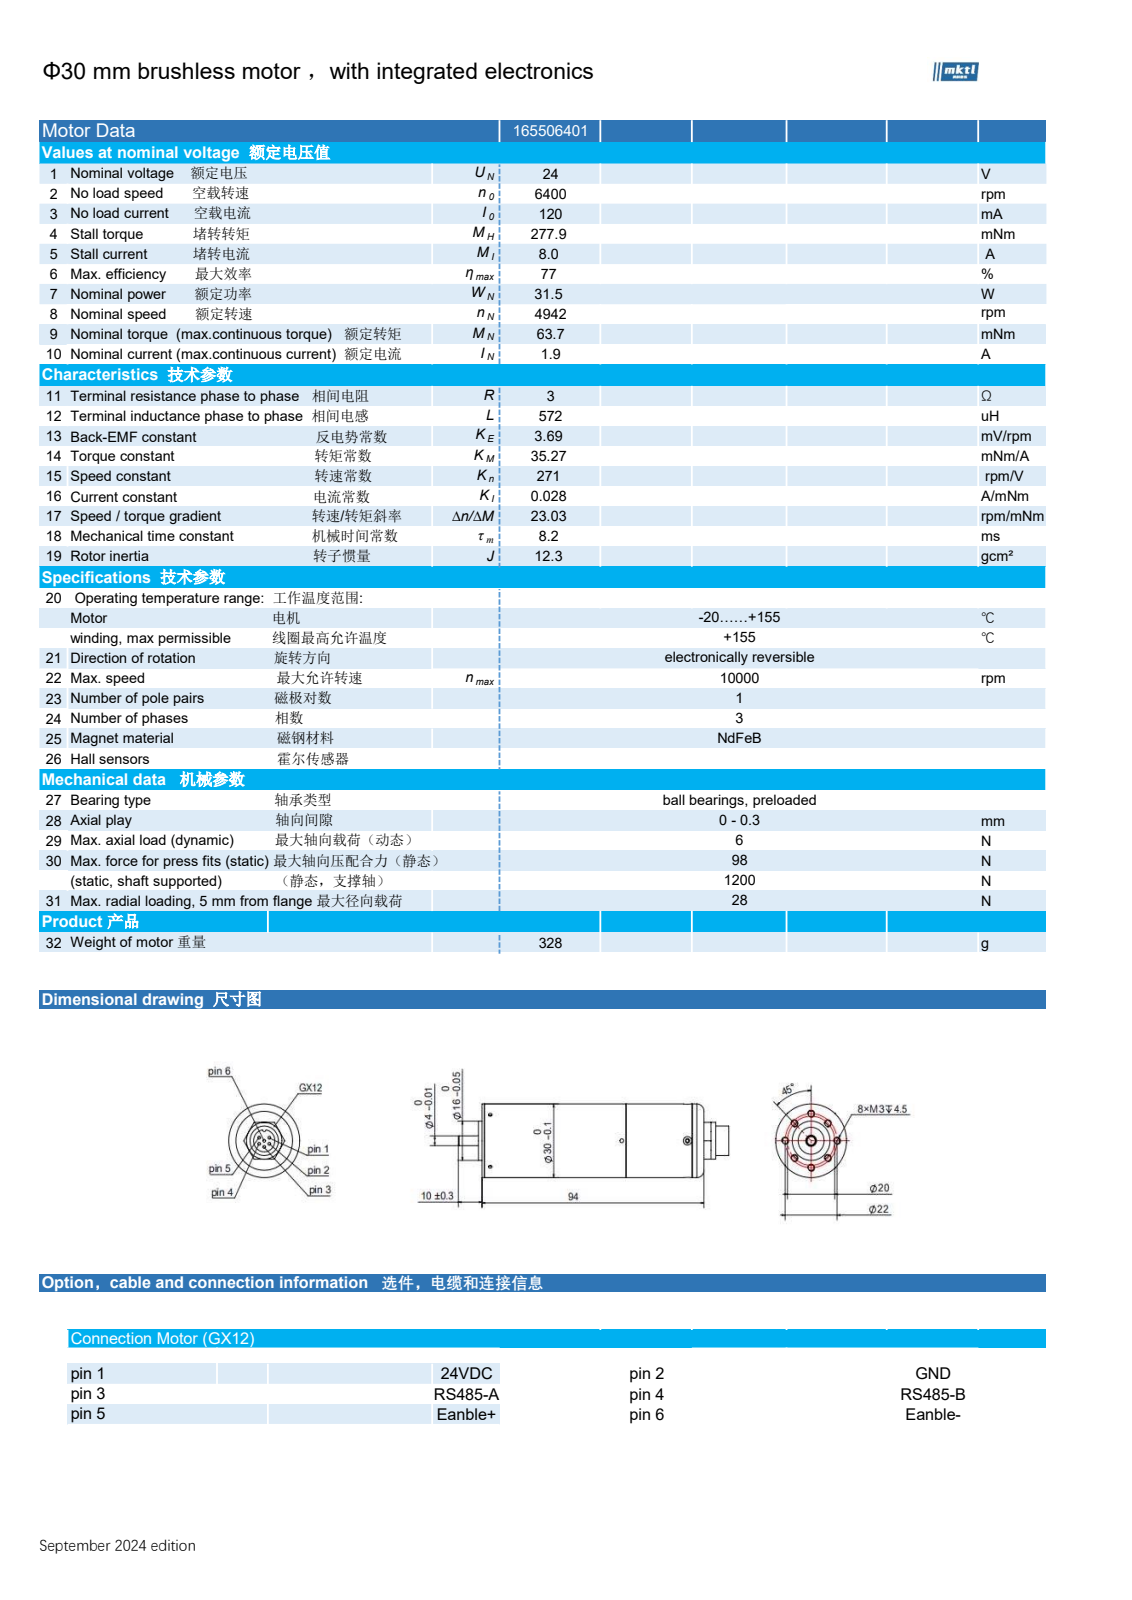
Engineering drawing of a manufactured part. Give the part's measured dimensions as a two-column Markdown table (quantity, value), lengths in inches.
| quantity | value |
| --- | --- |
| part name | approval 165506401 |
| STEP written by | SolidWorks 2018 (CONFIG_CONTROL_DESIGN) |
| units | inches |
| bodies | 240 solids, 1781 faces (558 planar, 1149 cylindrical, 74 other) |
| overall size | 4.508 × 1.181 × 1.181 |
| volume | 3.098 in³ |
| surface area | 276.2 in² |
| round holes (diameter × count) | 0.098 × 12, 0.043 × 6, 0.063 × 5, 0.047 × 3, 0.051 × 3, 0.039 × 2, 0.049 × 2, 0.067 × 2, 0.071 × 2, 0.087 × 2, 0.157 × 1, 0.354 × 1 |
| round bosses / shafts (diameter × count) | 0.047 × 6, 0.071 × 3, 0.055 × 3, 0.012 × 3, 1.181 × 1, 1.106 × 1, 1.102 × 1, 1.098 × 1 |
| partial cylindrical surfaces (radius × count) | 0.03 × 7, 0.02 × 4, 0.413 × 1, 0.478 × 1, 0.531 × 1 |
| main face-to-face distances | 0.016, 0.024, 0.031, 0.039, 0.055, 0.047, 0.063, 0.071, 0.079, 0.087 |
| hole center spacings | 0.764, 0.319, 0.059, 0.394, 0.433, 0.557, 0.613, 0.118 |
